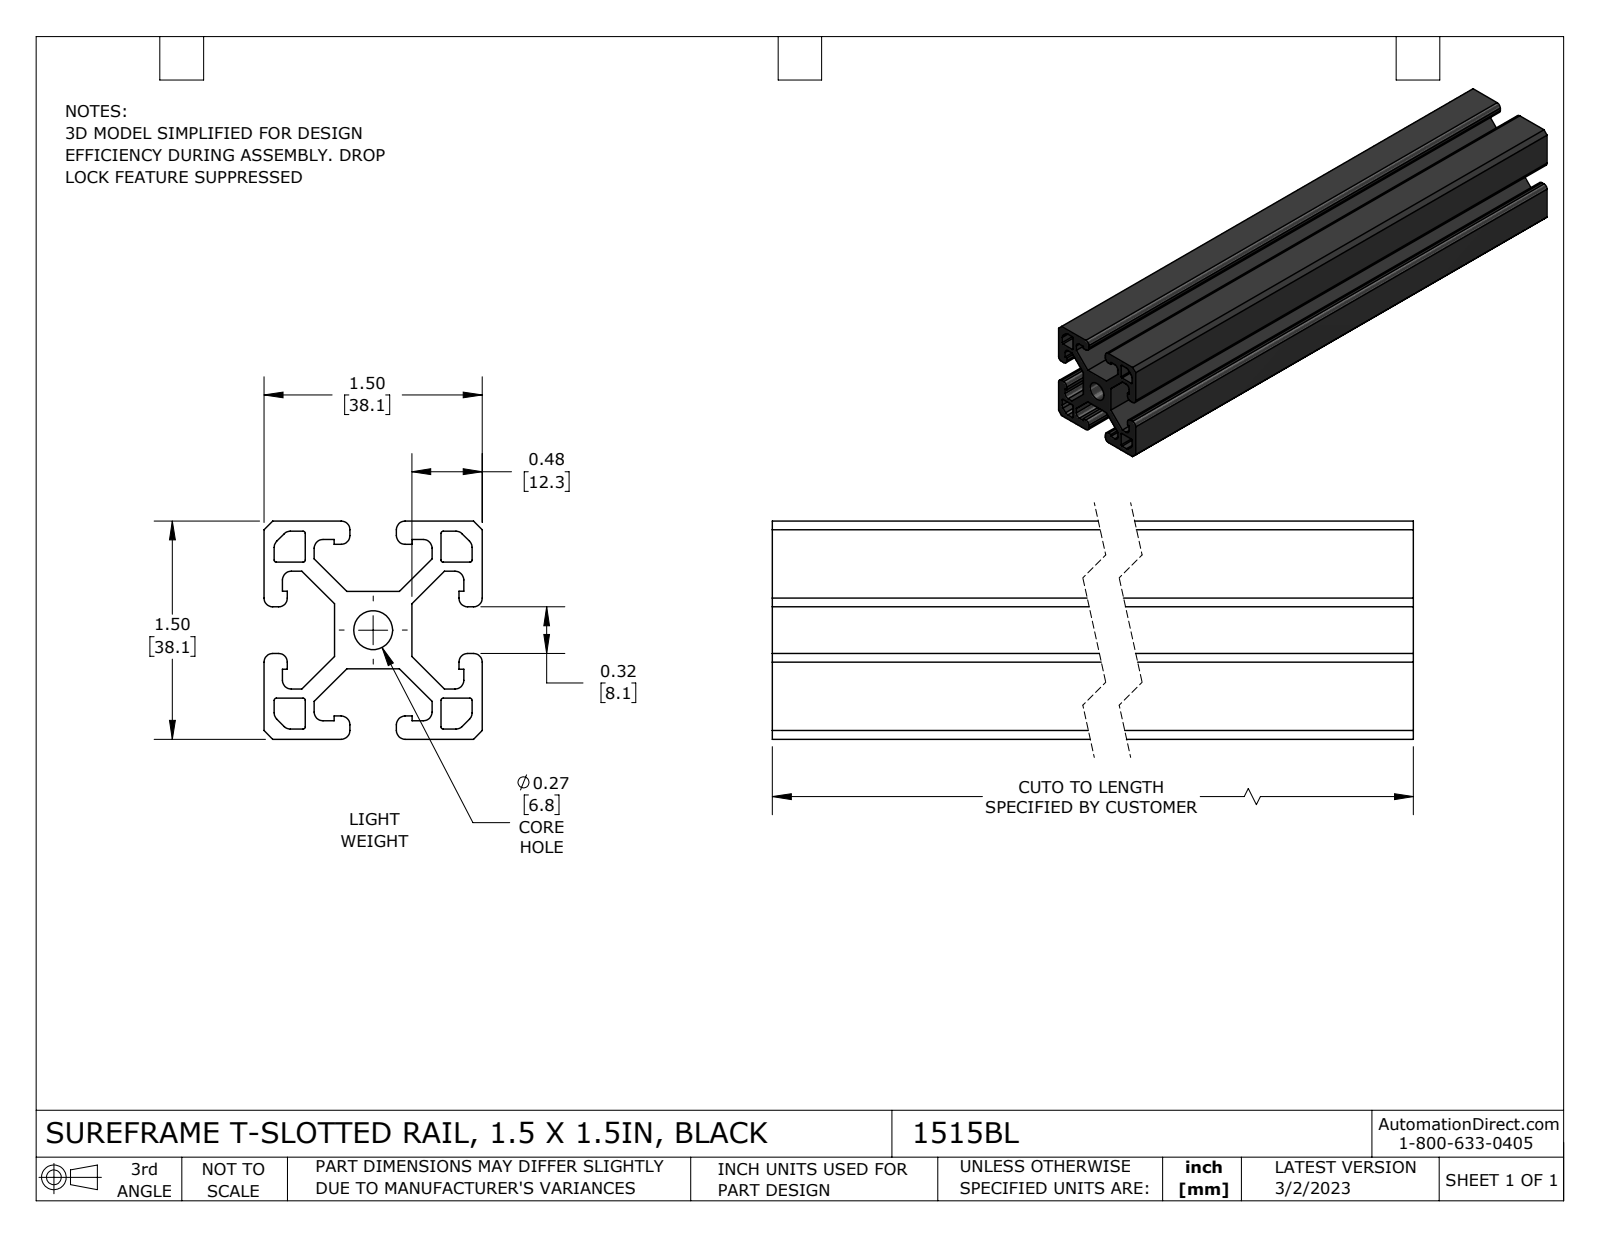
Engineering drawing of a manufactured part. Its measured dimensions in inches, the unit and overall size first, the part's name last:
Units: inches
Overall size (bounding box): 8 × 1.5 × 1.5
Round holes (diameter × count): ⌀0.268 ×1
Partial cylindrical surfaces — rounded edges, fillets, slot ends (radius × count): R0.06 ×32, R0.015 ×12
Main face-to-face distances: 1.5, 0.283, 1.217, 0.484, 1.016, 0.201, 0.733, 0.12, 0.934, 0.532
Volume: 7.396 in³ · Surface area: 133.5 in²
Bodies: 1 solid, 132 faces (86 planar, 46 cylindrical, 0 other)
Part name (STEP PRODUCT): 1515BL
STEP written by: SolidWorks 2021 (CONFIG_CONTROL_DESIGN)
